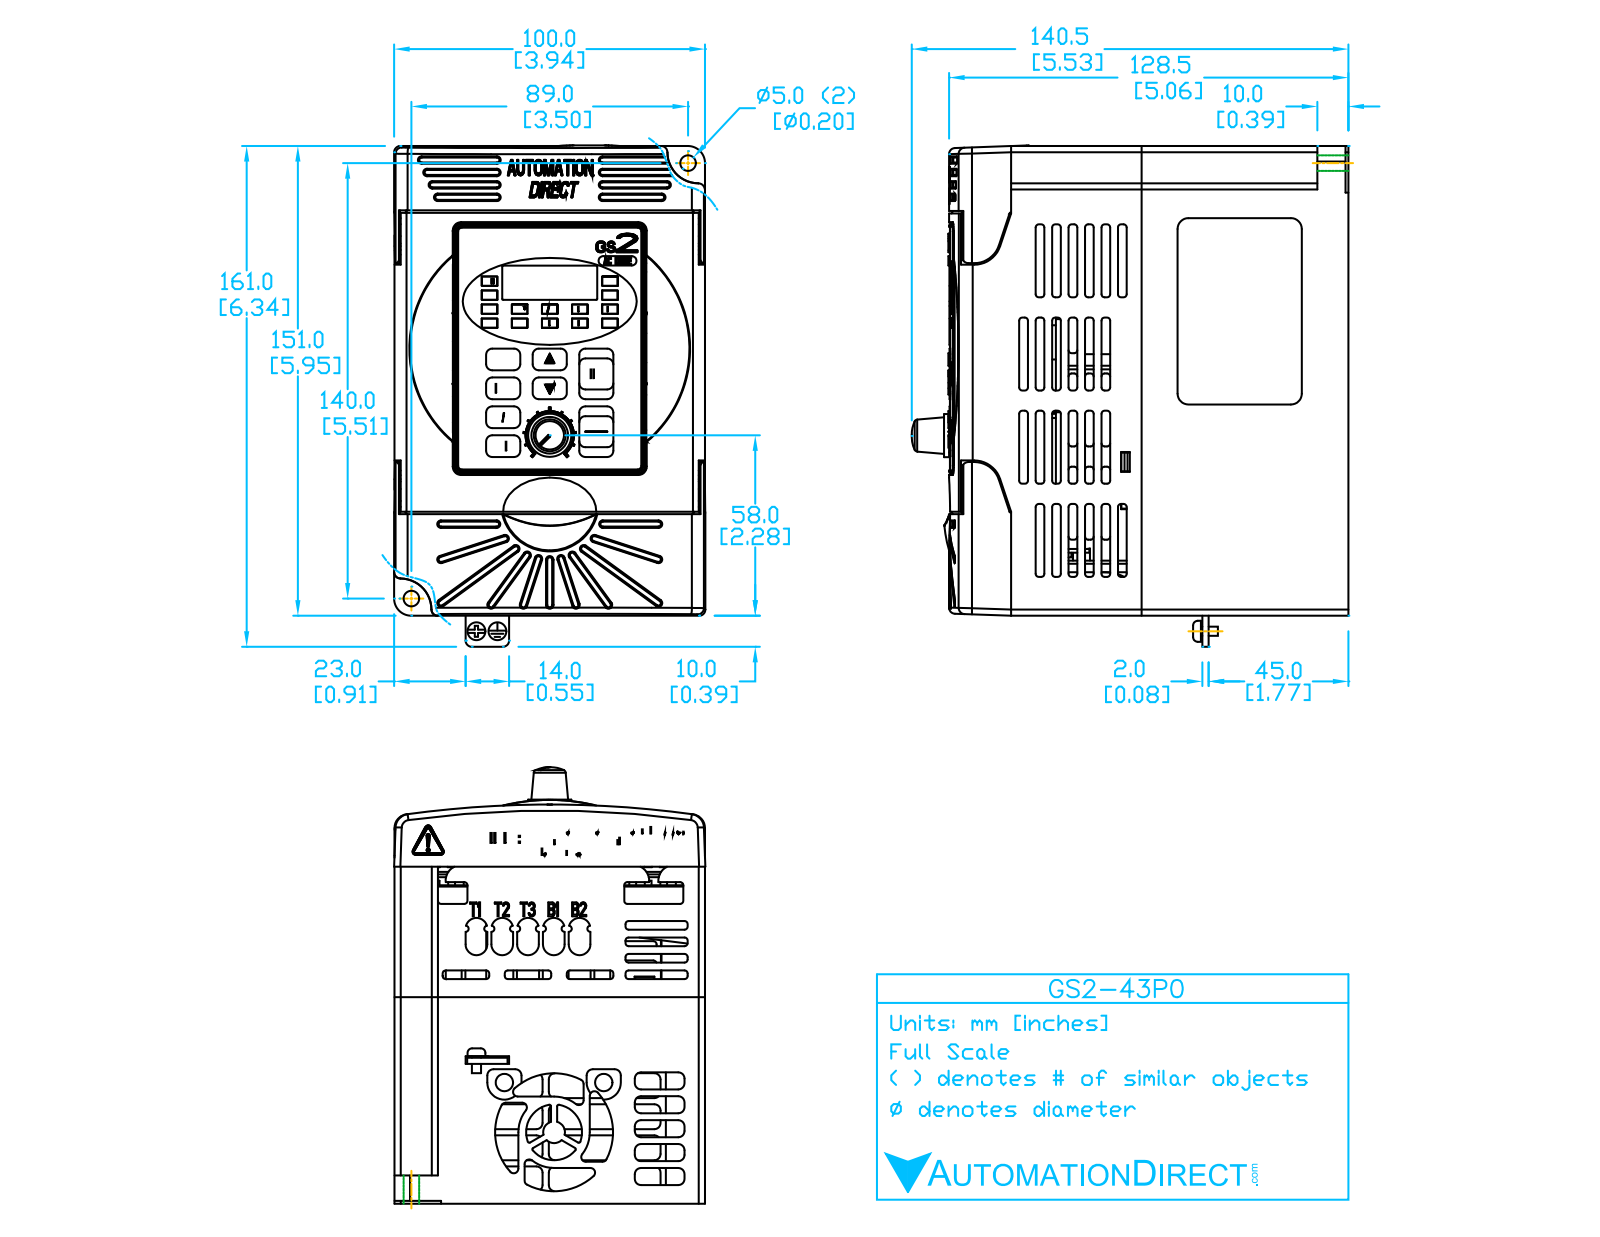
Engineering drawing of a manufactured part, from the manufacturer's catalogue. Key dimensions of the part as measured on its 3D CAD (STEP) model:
Part name (STEP PRODUCT): GS2-43P0
STEP written by: SolidWorks 2015 (AUTOMOTIVE_DESIGN)
Units: inches
Bodies: 1 solid, 749 faces (314 planar, 228 cylindrical, 207 other)
Overall size (bounding box): 6.345 × 5.495 × 3.94
Volume: 112.9 in³ · Surface area: 196.7 in²
Round holes (diameter × count): ⌀0.2 ×2, ⌀0.7 ×1, ⌀1.46 ×1
Round bosses / shafts (diameter × count): ⌀0.545 ×1, ⌀0.22 ×1, ⌀0.15 ×1
Partial cylindrical surfaces — rounded edges, fillets, slot ends (radius × count): R0.04 ×40, R0.06 ×24, R0.125 ×10, R0.02 ×8, R0.03 ×8, R0.045 ×6, R0.2 ×6, R0.1 ×4
Main face-to-face distances: 3.94, 5.95, 4.256, 4.266, 0.015, 5.935, 0.03, 0.761, 3.179, 0.03
Hole centre spacings: 6.528
